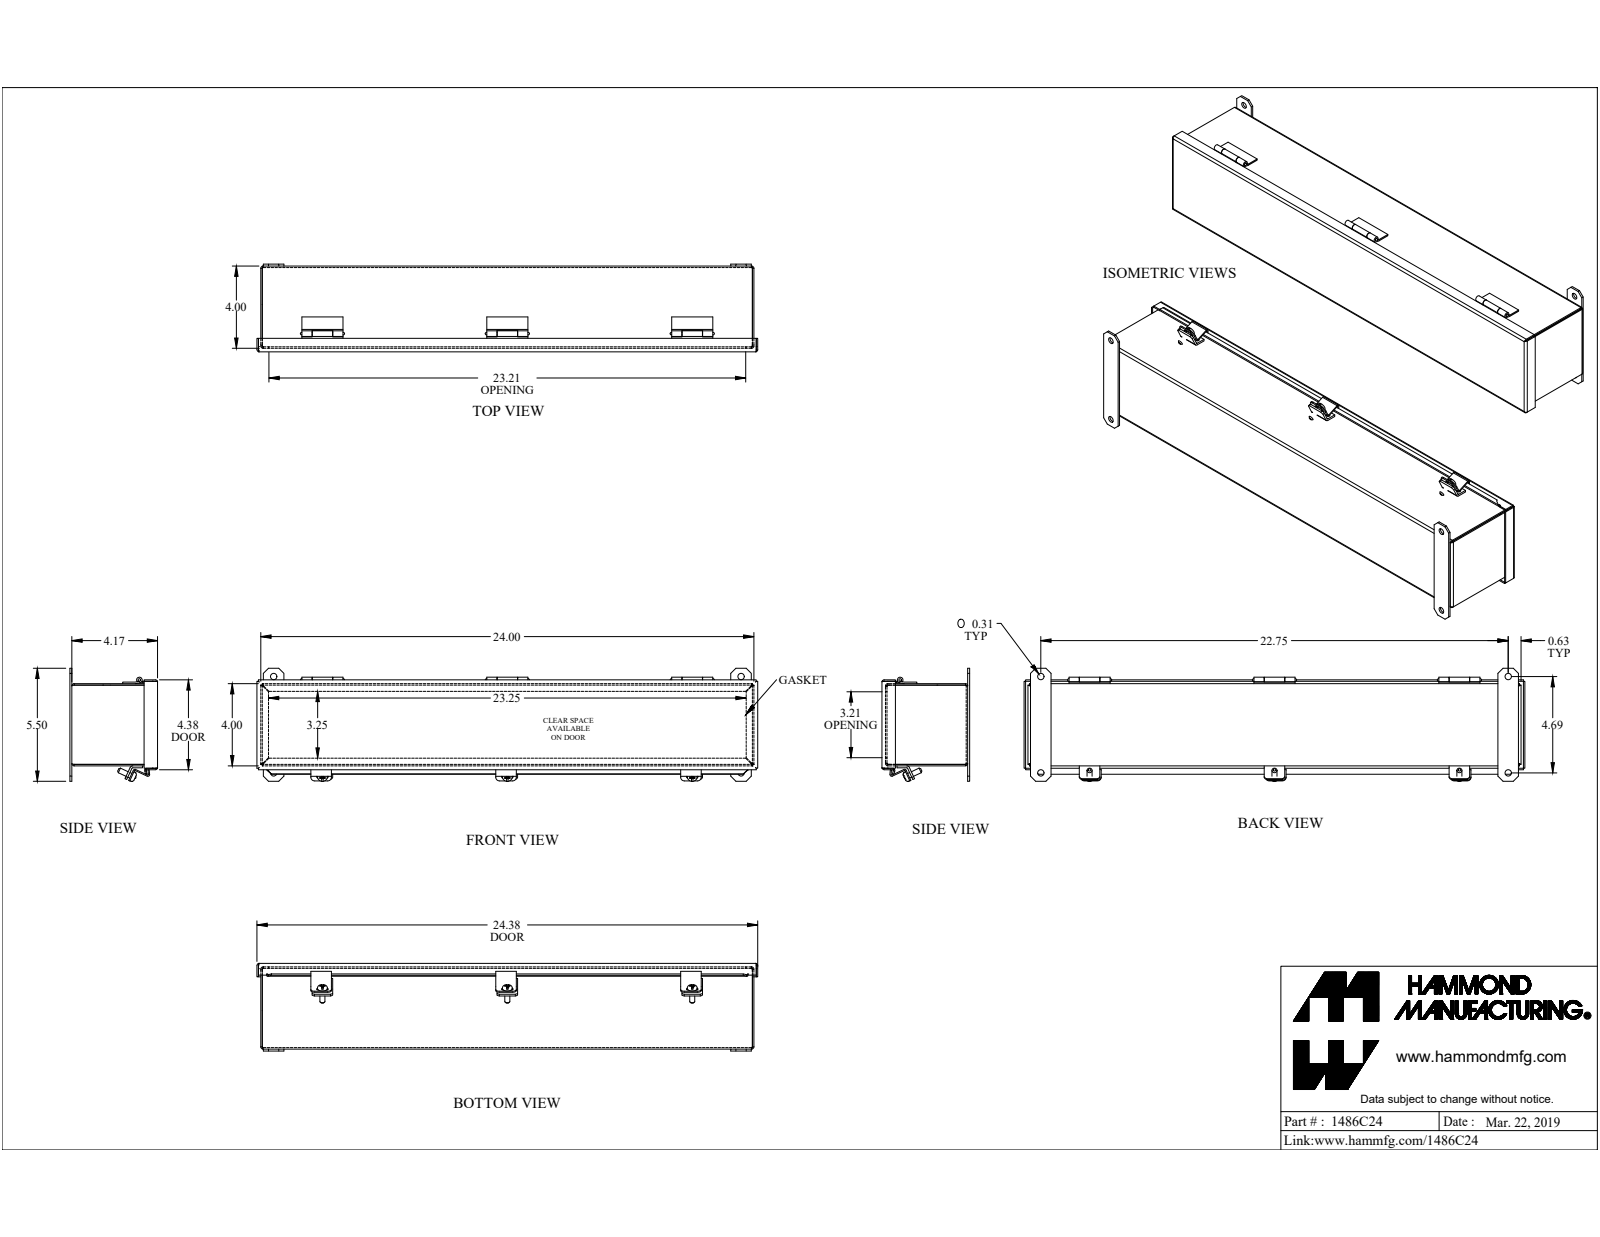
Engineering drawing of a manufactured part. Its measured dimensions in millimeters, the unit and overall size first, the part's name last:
Units: millimetres
Overall size (bounding box): 619.1 × 139.9 × 108.4
Round holes (diameter × count): ⌀8 ×4, ⌀5.4 ×3, ⌀3.2 ×1
Round bosses / shafts (diameter × count): ⌀12.2 ×3, ⌀6.2 ×3, ⌀7 ×1
Partial cylindrical surfaces — rounded edges, fillets, slot ends (radius × count): R0.9 ×13, R2.7 ×13, R4.8 ×12, R6.4 ×12, R0.3 ×6, R3.6 ×6, R0.7 ×2, R2.2 ×2
Main face-to-face distances: 1.8, 99.8, 104.1, 101.6, 97.9, 106, 102.3, 4.7, 6.6, 99.4
Hole centre spacings: 119.1, 228.6, 577.9, 590, 457.2
Volume: 723 300 mm³ · Surface area: 726 500 mm²
Bodies: 26 solids, 536 faces (355 planar, 124 cylindrical, 57 other)
Part name (STEP PRODUCT): 1486C24
STEP written by: SolidWorks 2019 (CONFIG_CONTROL_DESIGN)
